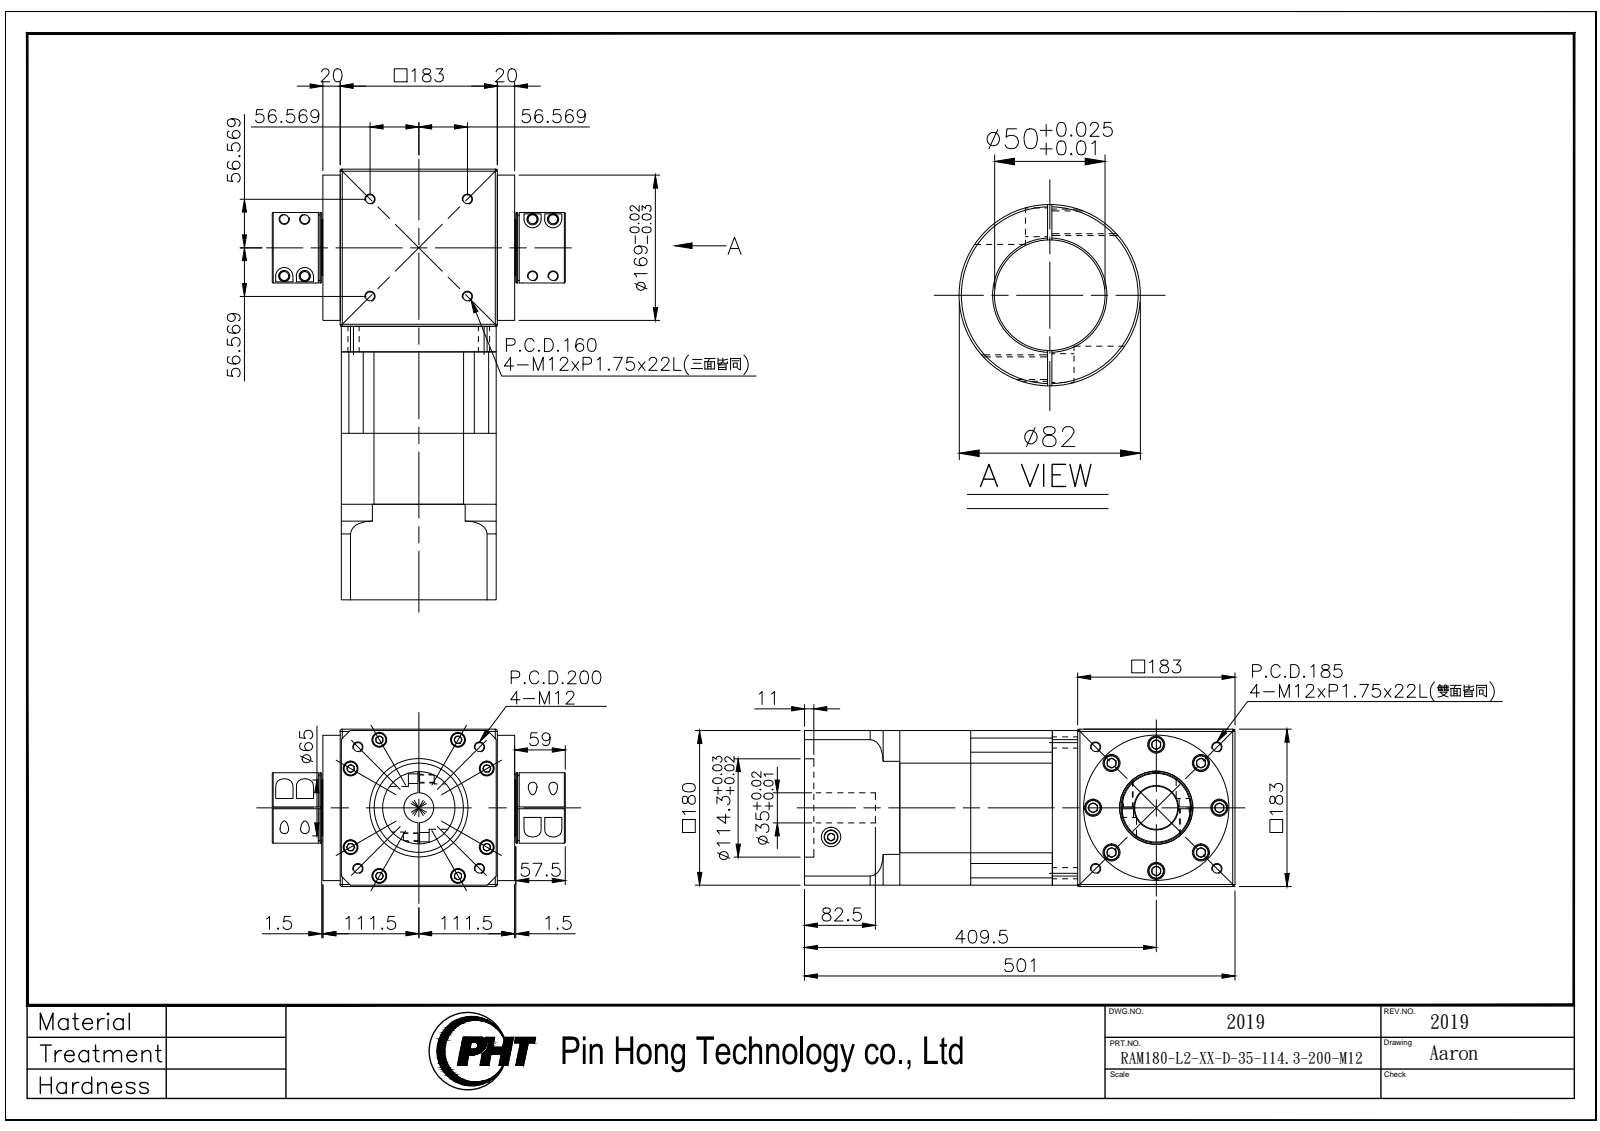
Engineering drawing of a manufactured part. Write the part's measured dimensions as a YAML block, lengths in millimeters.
part_name: "RA180-L2-XX-D-35-114.3-200-M12_2019"
step_written_by: "SolidWorks 2016 (AUTOMOTIVE_DESIGN)"
units: millimeters
bodies: {solids: 5, faces: 1065, planar: 481, cylindrical: 372, other: 212}
overall_size: [501, 341, 183]
volume: 16150000
surface_area: 994334
round_holes:
  - {diameter: 10.2, count: 20}
  - {diameter: 13, count: 12}
  - {diameter: 11, count: 8}
  - {diameter: 14, count: 8}
  - {diameter: 17, count: 8}
  - {diameter: 20, count: 8}
  - {diameter: 22.5, count: 2}
  - {diameter: 35, count: 1}
  - {diameter: 50, count: 1}
  - {diameter: 50.6, count: 1}
  - {diameter: 56.5, count: 1}
  - {diameter: 104, count: 1}
round_bosses_or_shafts:
  - {diameter: 18, count: 12}
  - {diameter: 18.3, count: 8}
  - {diameter: 16, count: 8}
  - {diameter: 12, count: 8}
  - {diameter: 169, count: 1}
  - {diameter: 160, count: 1}
  - {diameter: 85, count: 1}
  - {diameter: 84, count: 1}
partial_cylinders:
  - {radius: 10, count: 8}
  - {radius: 12.5, count: 4}
  - {radius: 104, count: 1}
  - {radius: 105, count: 1}
  - {radius: 120, count: 1}
face_to_face_distances: [1.5, 181.5, 180, 183, 82.5, 177.5, 95, 207, 124.5, 29.5]
hole_center_spacings: [91.5, 25.12, 26.38, 30.43, 56.25, 65.91, 73.5, 103.94]
